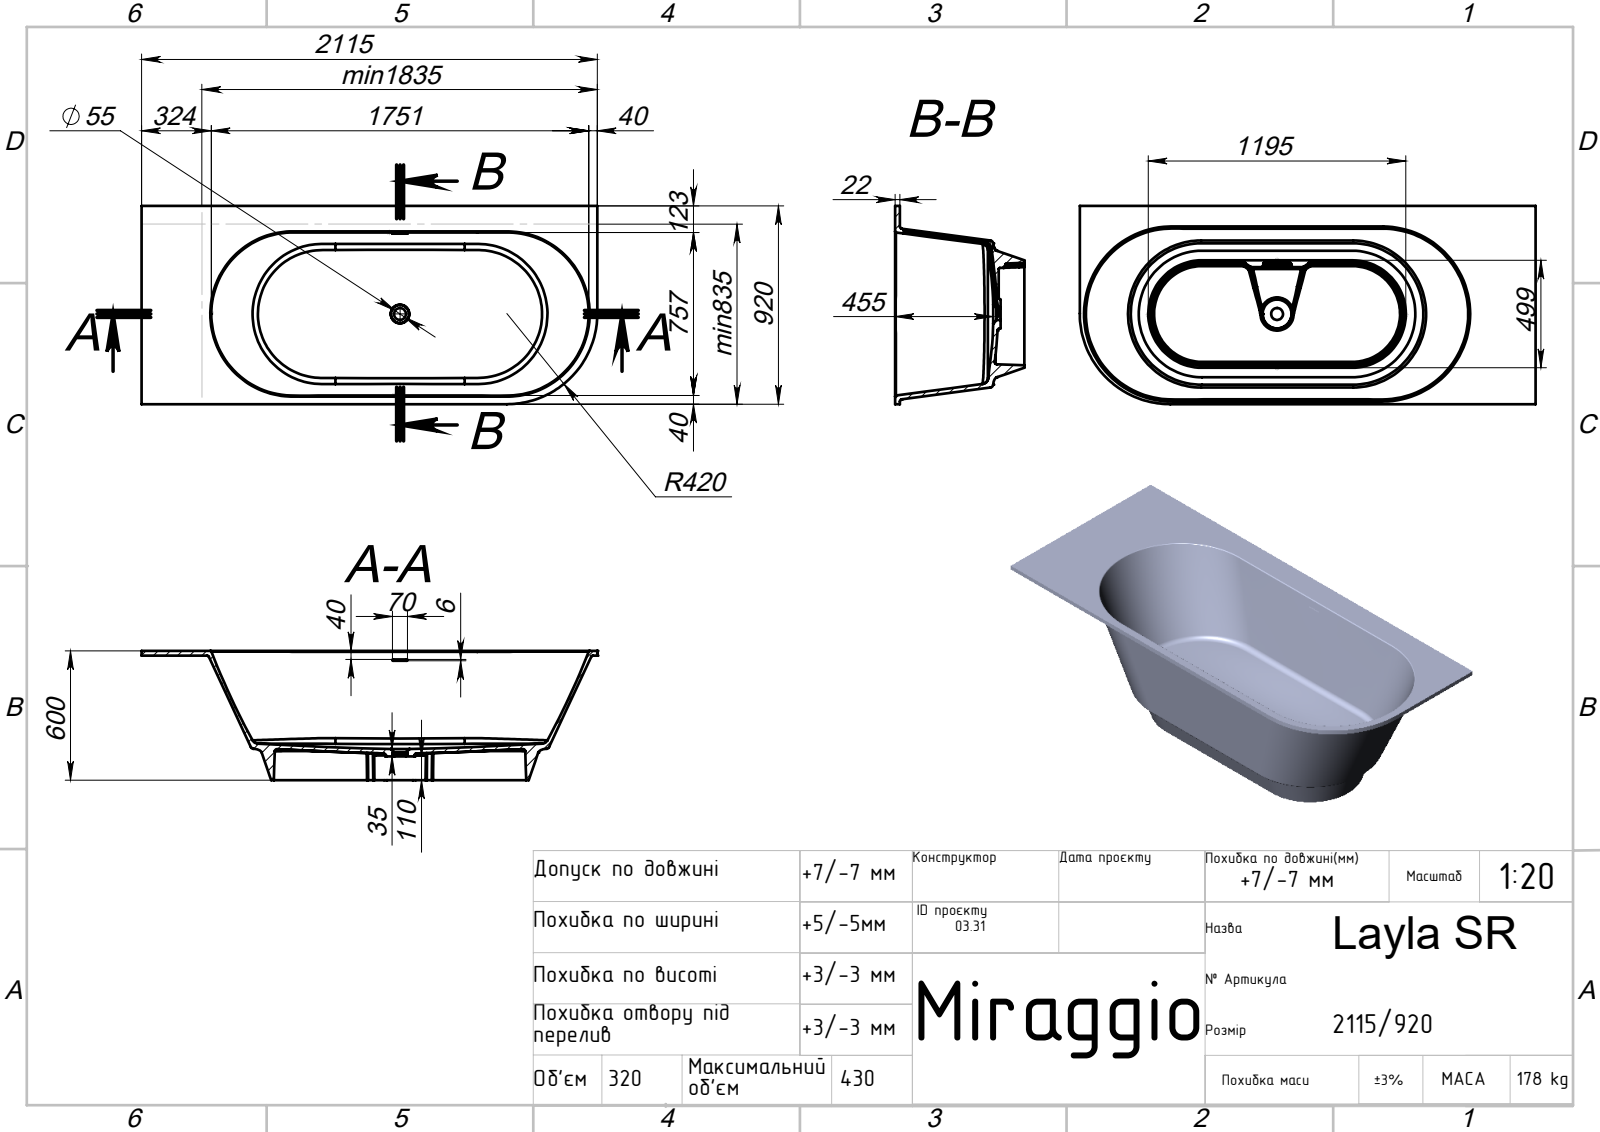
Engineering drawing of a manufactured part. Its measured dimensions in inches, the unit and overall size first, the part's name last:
Units: inches
Overall size (bounding box): 83.268 × 36.22 × 23.622
Round holes (diameter × count): ⌀2.165 ×1
Partial cylindrical surfaces — rounded edges, fillets, slot ends (radius × count): R0.394 ×4, R0.197 ×3, R0.118 ×2, R1.457 ×1, R1.811 ×1, R2.461 ×1, R7.818 ×1, R9.341 ×1
Main face-to-face distances: 0.866, 22.756, 23.622, 36.22, 4.685, 18.071, 18.937, 4.331, 0.354, 18.425
Volume: 4 934 in³ · Surface area: 11 440 in²
Bodies: 1 solid, 125 faces (28 planar, 19 cylindrical, 78 other)
Part name (STEP PRODUCT): Layla SR
STEP written by: SolidWorks 2020 (AUTOMOTIVE_DESIGN)
